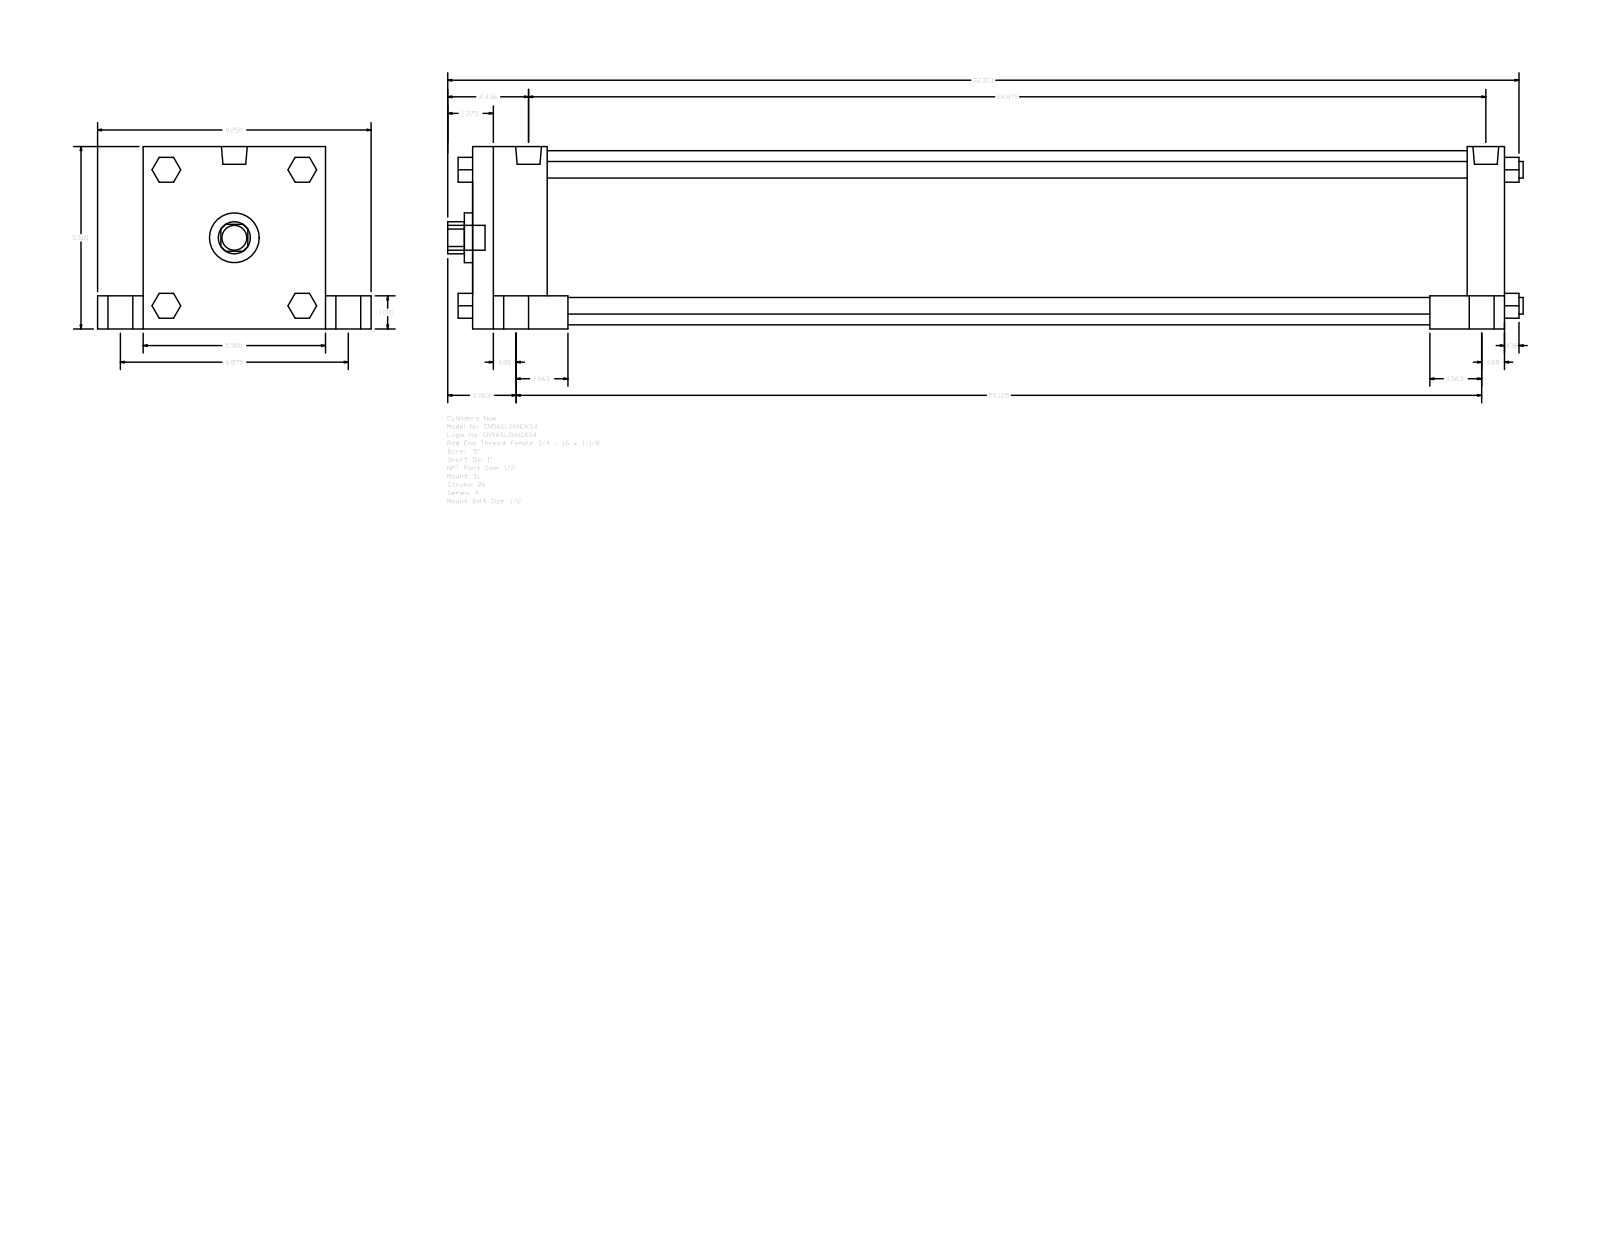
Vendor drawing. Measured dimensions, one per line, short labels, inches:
name: A_SL__0500_1
written by: GSSL Pune (CONFIG_CONTROL_DESIGN)
unit: in
bodies: 0 solids, 150 faces (114 planar, 36 cylindrical, 0 other)
size: 32.437 × 8.25 × 5.5
holes: 1× ⌀1, 1× ⌀1.5, 1× ⌀5.25
bosses: 5× ⌀0.75, 4× ⌀1, 4× ⌀0.5, 4× ⌀0.344, 2× ⌀0.778
rounds: 1× R0.484
face distances: 5.5, 31.125, 1.125, 1, 4.5, 1.375, 6.875, 2.25, 30, 27.75
